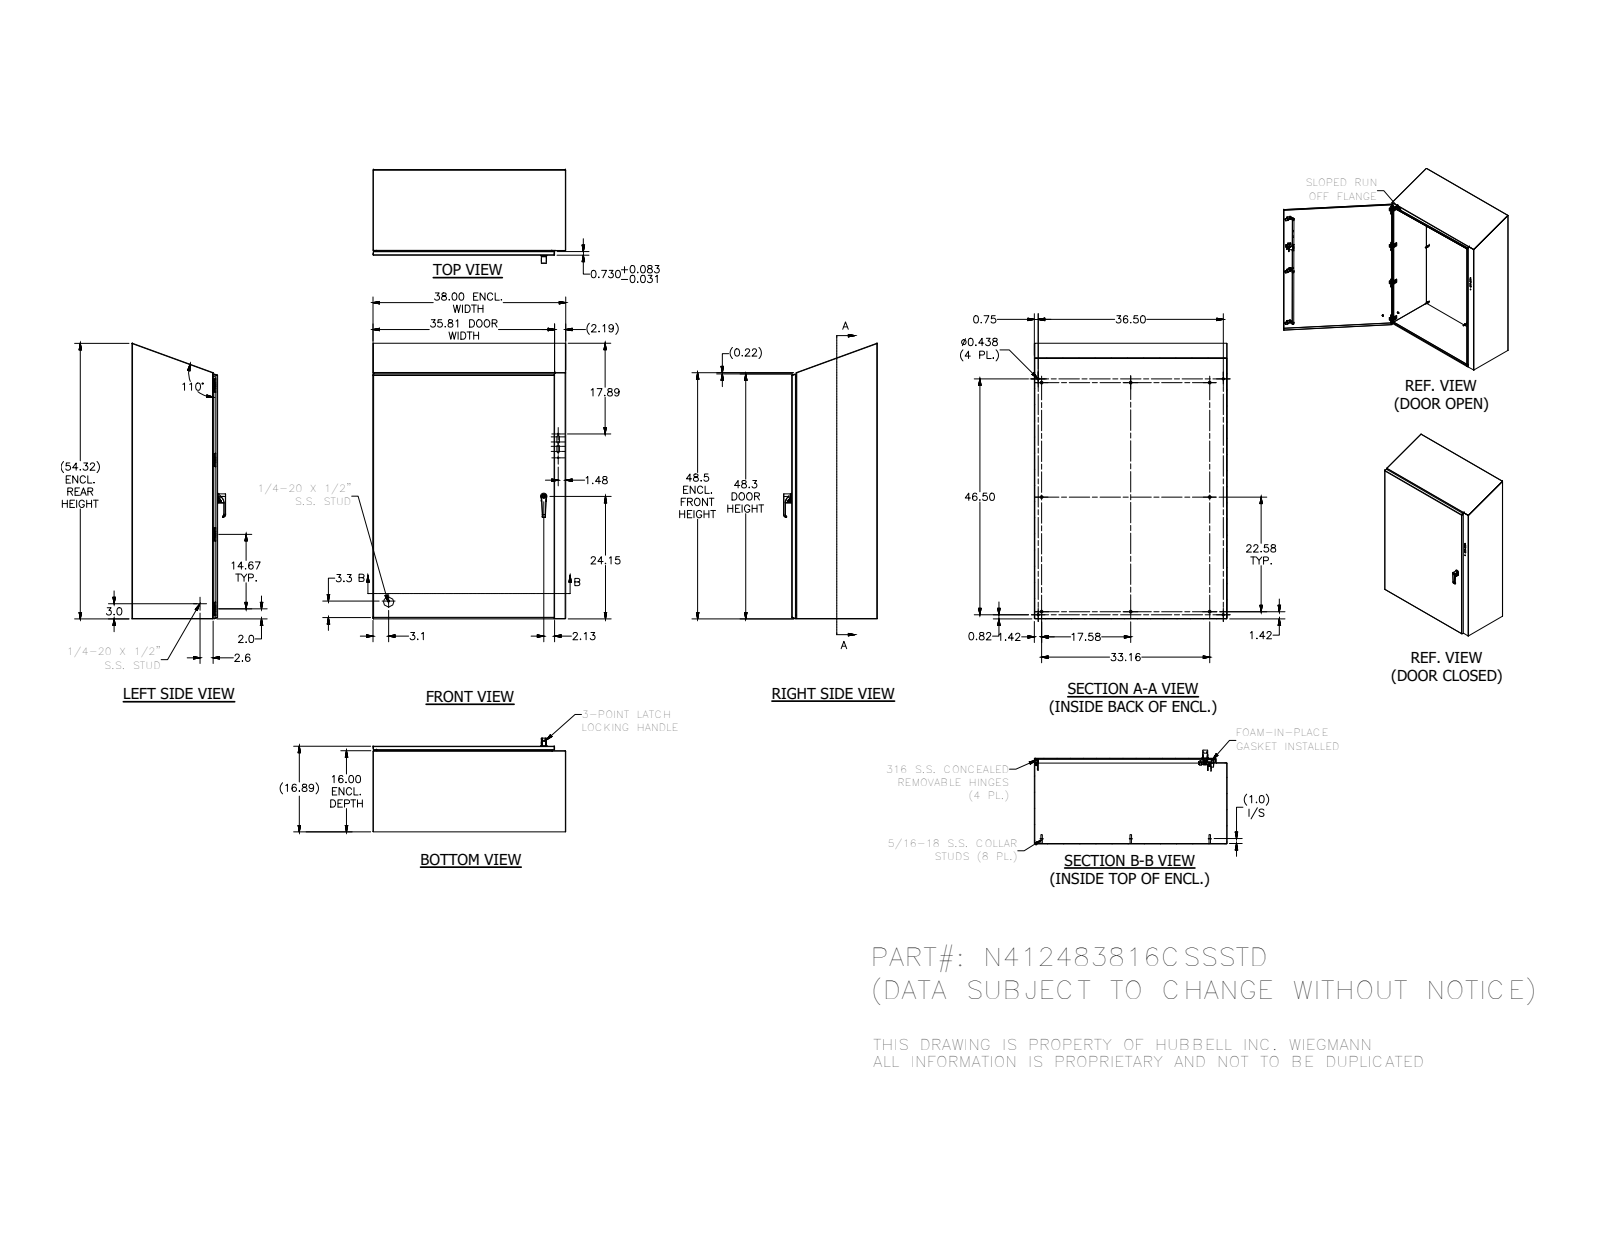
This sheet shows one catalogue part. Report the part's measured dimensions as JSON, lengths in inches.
{"part_name": "N412483816CSSSTDBLR; 388151; N4123816CSSSTDTOP; 38846 (+8 more)", "step_written_by": "Autodesk Inventor 2016 (AUTOMOTIVE_DESIGN)", "units": "inches", "bodies": {"solids": 91, "faces": 3097, "planar": 1170, "cylindrical": 1131, "other": 796}, "overall_size": [54.343, 38, 18.481], "volume_in3": 538, "surface_area_in2": 14480, "round_holes": [[0.093, 8], [0.152, 8], [0.167, 8], [0.172, 8], [0.187, 8], [0.145, 6], [0.156, 5], [0.32, 4], [0.437, 4], [0.196, 3], [0.211, 3], [0.22, 3]], "round_bosses_or_shafts": [[0.25, 20], [0.3, 14], [0.563, 8], [0.36, 8], [0.32, 8], [0.275, 8], [0.256, 8], [0.164, 8]], "partial_cylinders_radius": [[0.05, 50], [0.125, 45], [0.02, 38], [0.031, 36], [0.016, 34], [0.012, 31], [0.025, 24], [0.105, 18]], "face_to_face_distances": [0.074, 16.813, 16.739, 16.887, 37.926, 37.852, 38, 15.926, 0.887, 0.813], "hole_center_spacings": [14.667, 14.667, 29.333, 14.007, 29.333, 44, 0.5, 0.656]}
